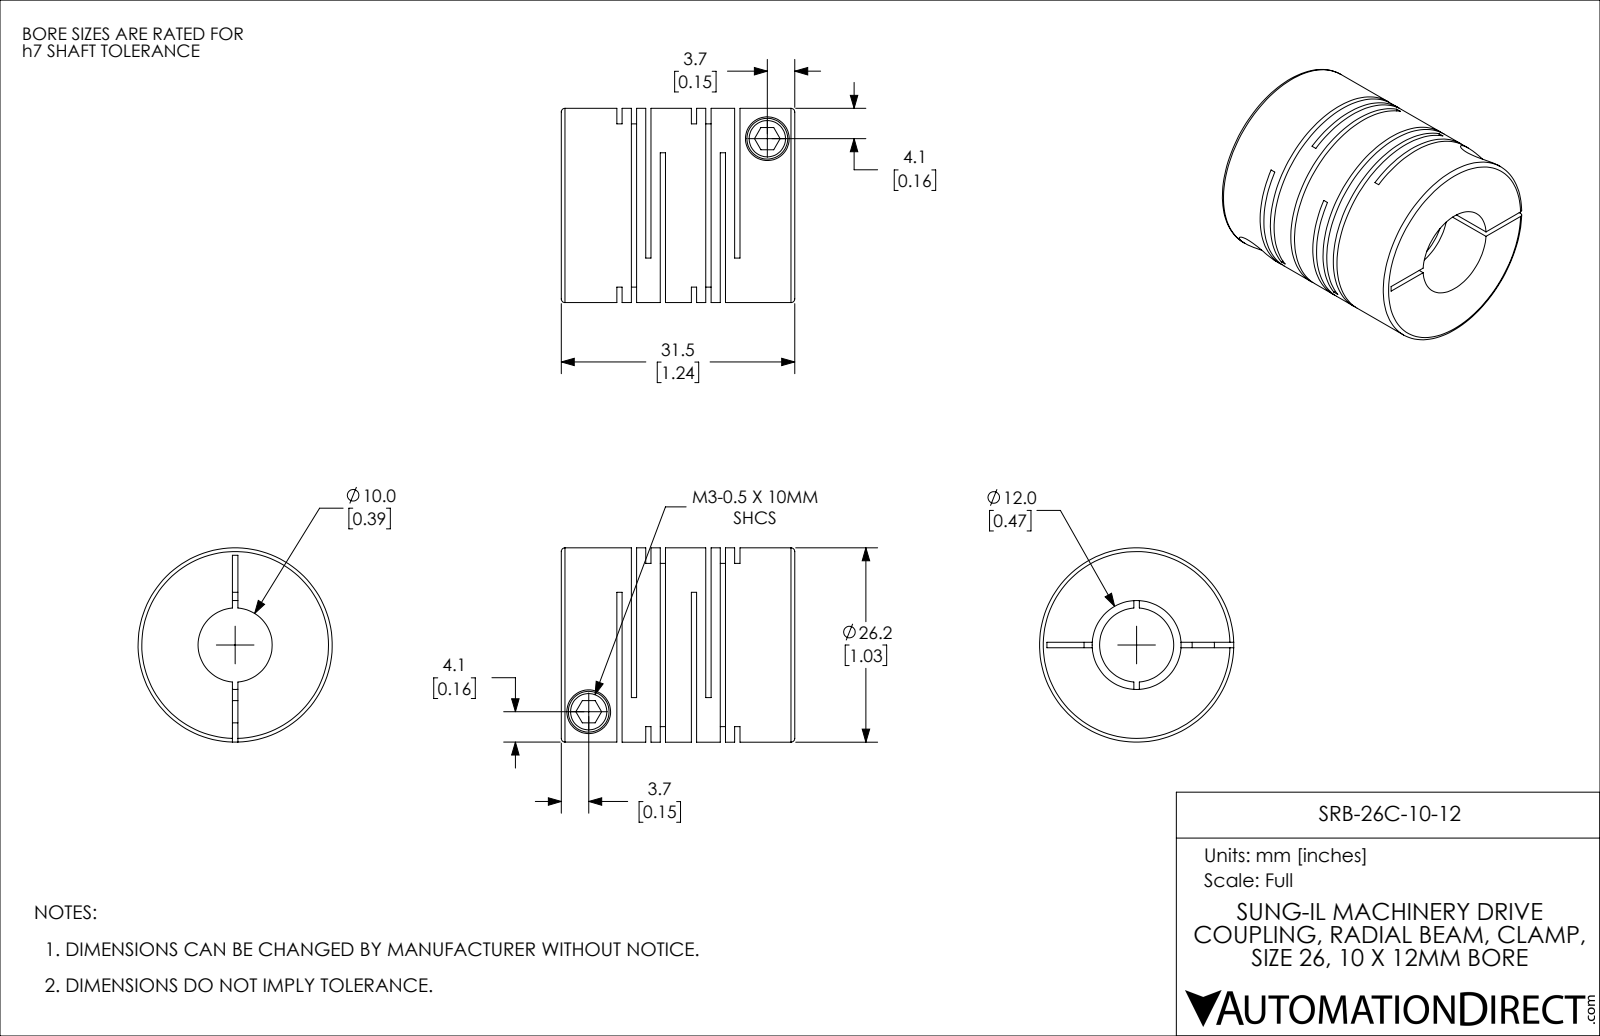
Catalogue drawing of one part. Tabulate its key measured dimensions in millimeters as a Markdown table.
| quantity | value |
| --- | --- |
| part name | SRB-26C-10-12 |
| STEP written by | SolidWorks 2021 (CONFIG_CONTROL_DESIGN) |
| units | millimeters |
| bodies | 1 solid, 114 faces (60 planar, 42 cylindrical, 12 other) |
| overall size | 31.5 × 26.2 × 26.2 |
| volume | 11 321 mm³ |
| surface area | 10 261 mm² |
| round holes (diameter × count) | 3 × 2, 5.9 × 2, 10 × 1, 12 × 1 |
| round bosses / shafts (diameter × count) | 5.5 × 2, 26.2 × 1 |
| main face-to-face distances | 1.95, 10.05, 0.71, 3.9, 8.1, 12, 1.24, 2.66, 9.34, 13.95 |
